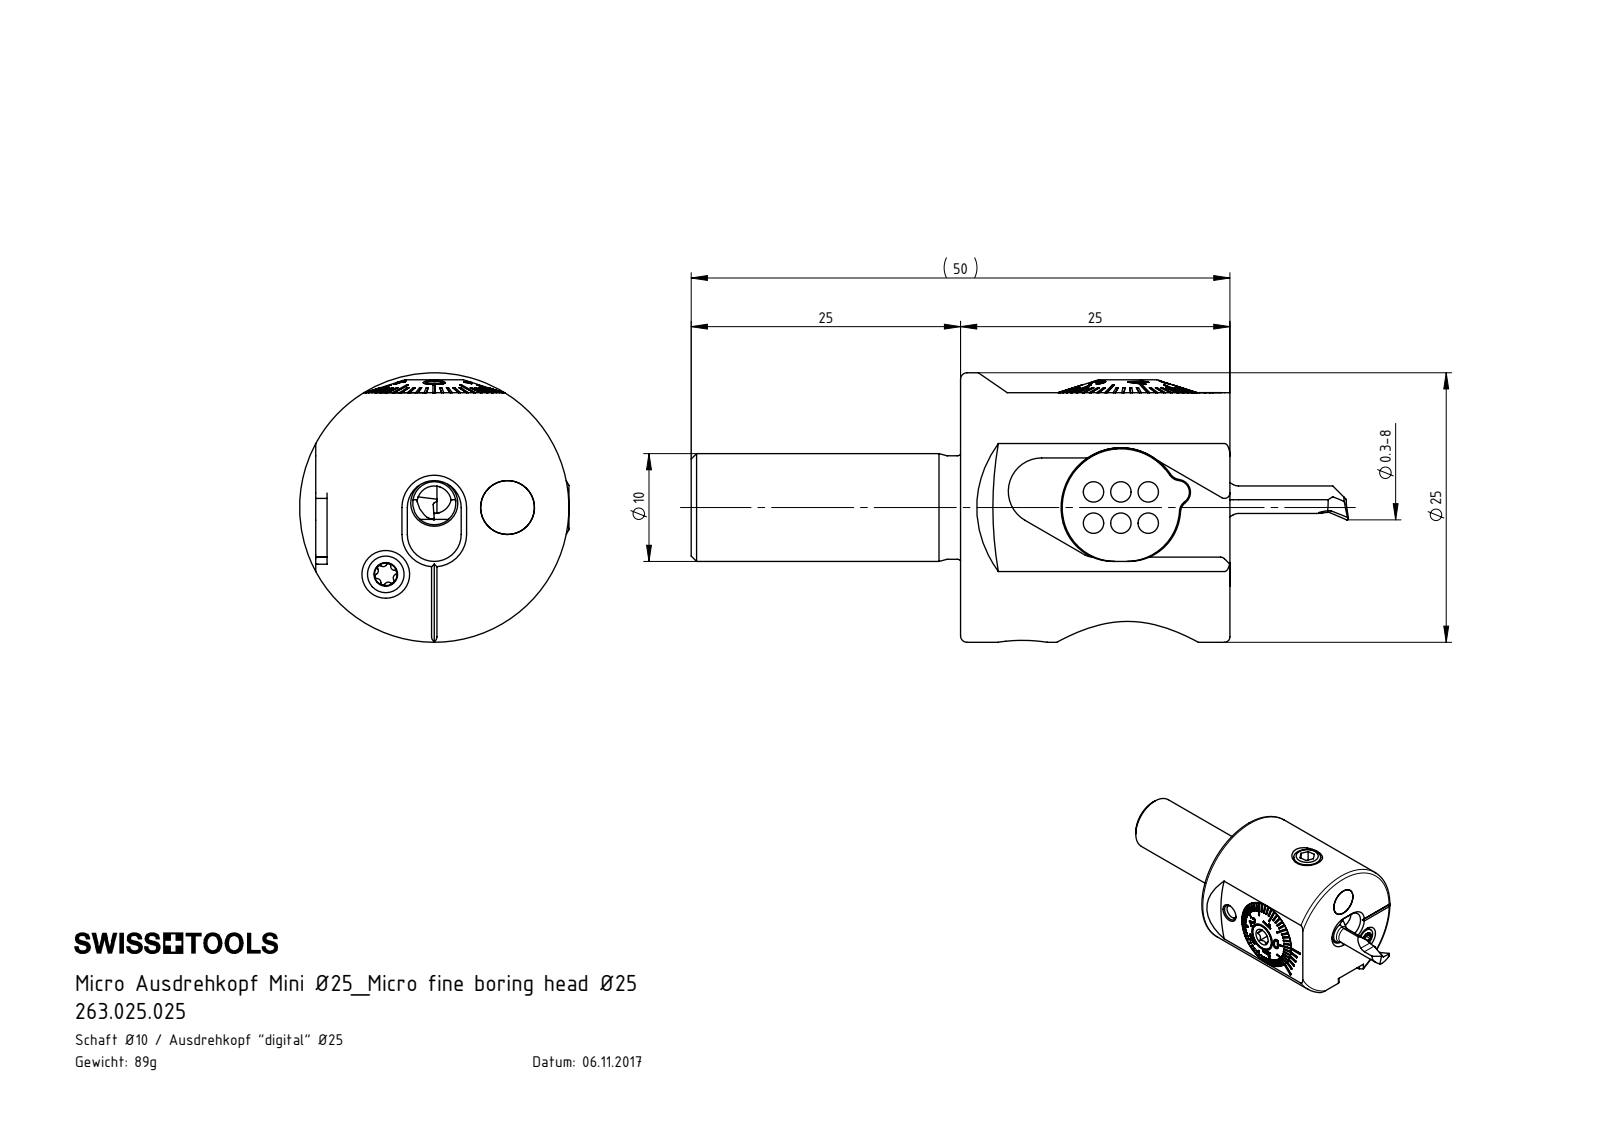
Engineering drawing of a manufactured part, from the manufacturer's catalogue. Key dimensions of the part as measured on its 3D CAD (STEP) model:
Part name (STEP PRODUCT): Fxx-MAB.xxx.xxx_A_F25x1x2; ISO 4026 - M4 x 8; Axx-BG4.003.xxx_A; F25-BG2.013.004_A (+8 more)
STEP written by: SolidWorks 2017 (AUTOMOTIVE_DESIGN)
Units: millimetres
Bodies: 17 solids, 805 faces (353 planar, 174 cylindrical, 278 other)
Overall size (bounding box): 50.01 × 25 × 25
Volume: 11 575 mm³ · Surface area: 9 650 mm²
Round holes (diameter × count): ⌀5 ×4, ⌀2 ×3, ⌀3.3 ×3, ⌀0.7 ×1, ⌀1 ×1, ⌀2.4 ×1, ⌀2.7 ×1, ⌀3 ×1, ⌀4 ×1, ⌀4.2 ×1, ⌀6.75 ×1, ⌀7.3 ×1
Round bosses / shafts (diameter × count): ⌀1.9 ×6, ⌀4.95 ×2, ⌀4 ×2, ⌀25 ×1, ⌀13 ×1, ⌀12.98 ×1, ⌀12.85 ×1, ⌀10.65 ×1
Partial cylindrical surfaces — rounded edges, fillets, slot ends (radius × count): R0.21 ×6, R0.36 ×5, R0.2 ×4, R2.2 ×4, R0.5 ×3, R1.1 ×3, R1.2 ×3, R2.5 ×2
Main face-to-face distances: 25, 1.5, 0.8, 3.9, 3.1, 3.8, 1.6, 5.6, 2.35, 4.1
Hole centre spacings: 5.48, 9.25, 0.4, 0.68, 2.6, 2.61, 3.5, 4.97
